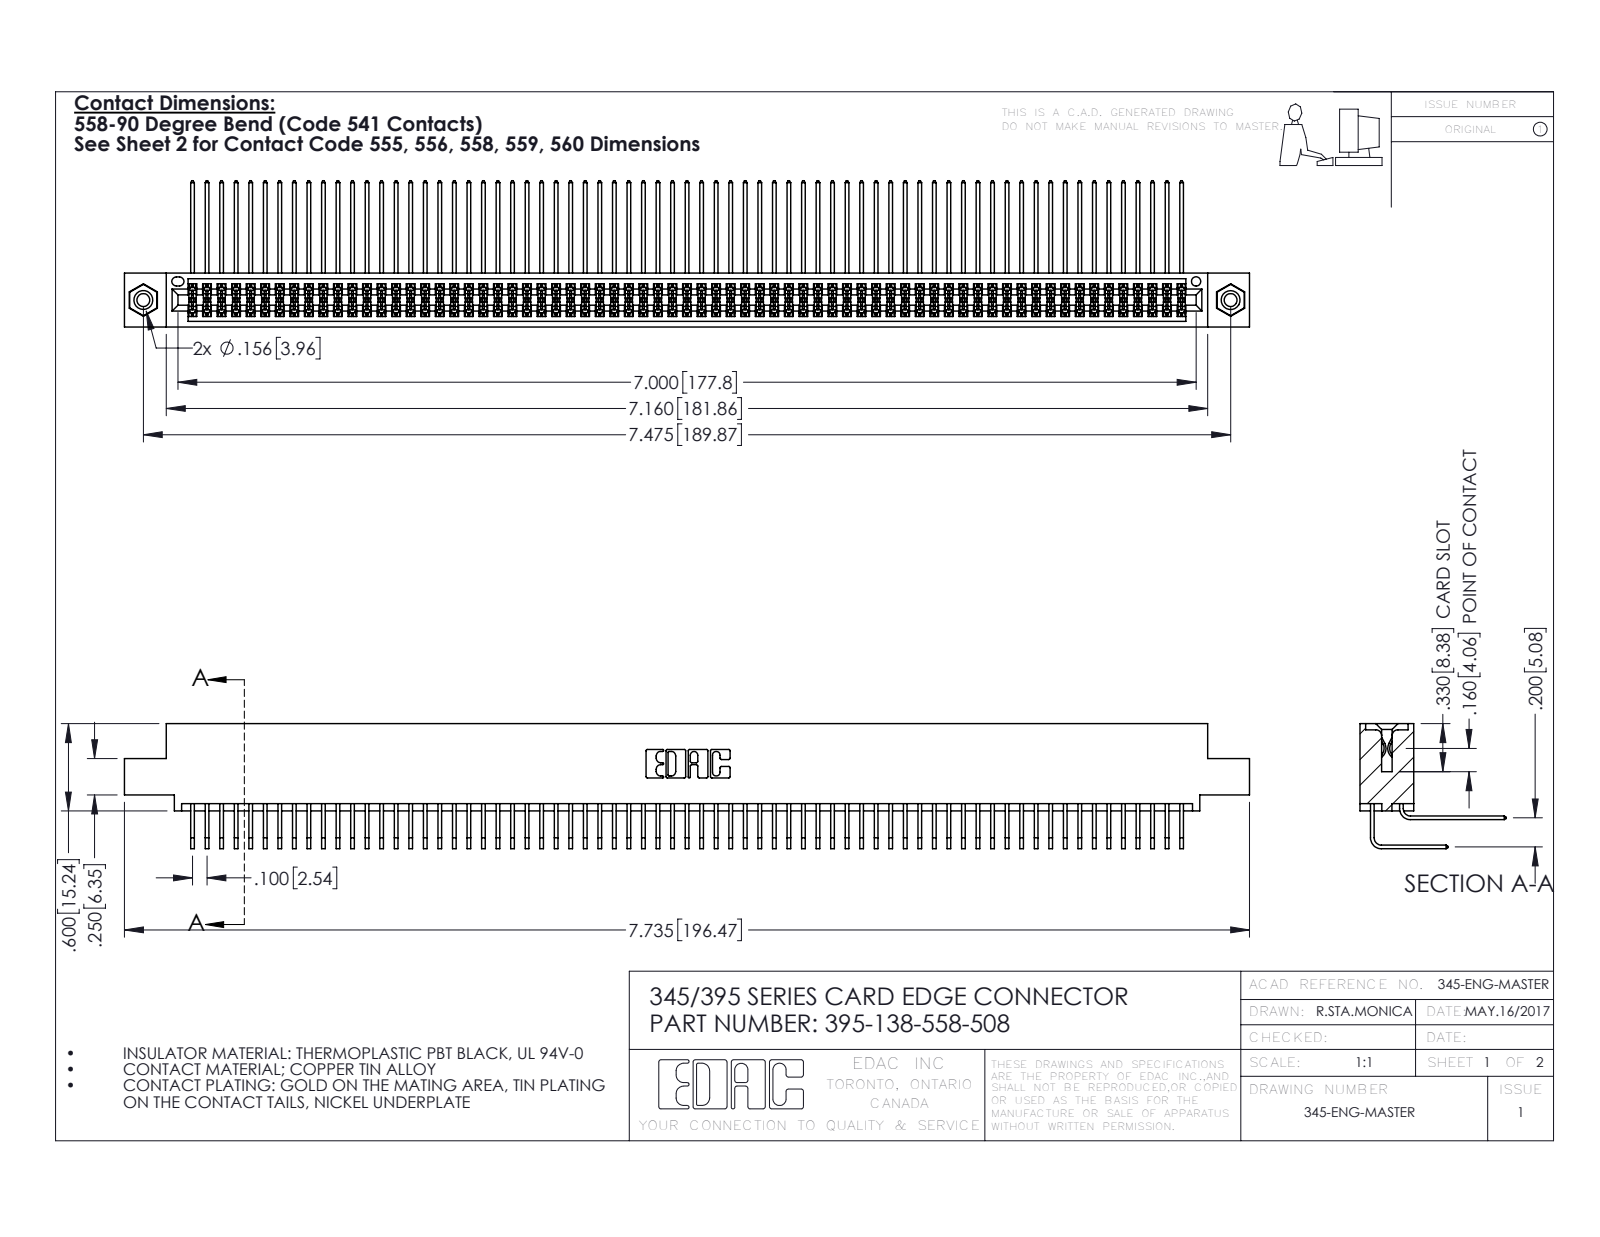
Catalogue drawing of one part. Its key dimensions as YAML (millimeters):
part_name: "345-292-001_558 Tail - 2; 345 Part_0.110 Offset - 0.156 Dia-TI; 395-138-558-508; 345-250-001_345-250-003-102 (+1 more)"
step_written_by: "SolidWorks 2016 (CONFIG_CONTROL_DESIGN)"
units: millimeters
bodies: {solids: 141, faces: 7366, planar: 4946, cylindrical: 2404, other: 16}
overall_size: [196.5, 25.5, 21.8]
volume: 20060
surface_area: 34010
round_holes:
  - {diameter: 2.3, count: 2}
  - {diameter: 3.2, count: 2}
  - {diameter: 4, count: 2}
  - {diameter: 1.6, count: 1}
round_bosses_or_shafts:
  - {diameter: 3.9, count: 2}
partial_cylinders:
  - {radius: 0.2, count: 275}
  - {radius: 0.3, count: 22}
  - {radius: 0.2, count: 6}
  - {radius: 0.8, count: 6}
  - {radius: 0.7, count: 3}
  - {radius: 0.4, count: 2}
  - {radius: 0.5, count: 2}
  - {radius: 0.6, count: 2}
face_to_face_distances: [1.8, 7.6, 5.1, 9.4, 2.5, 6.9, 0.6, 5.7, 0.6, 4.4]
hole_center_spacings: [6.9, 183.9, 189.9]
